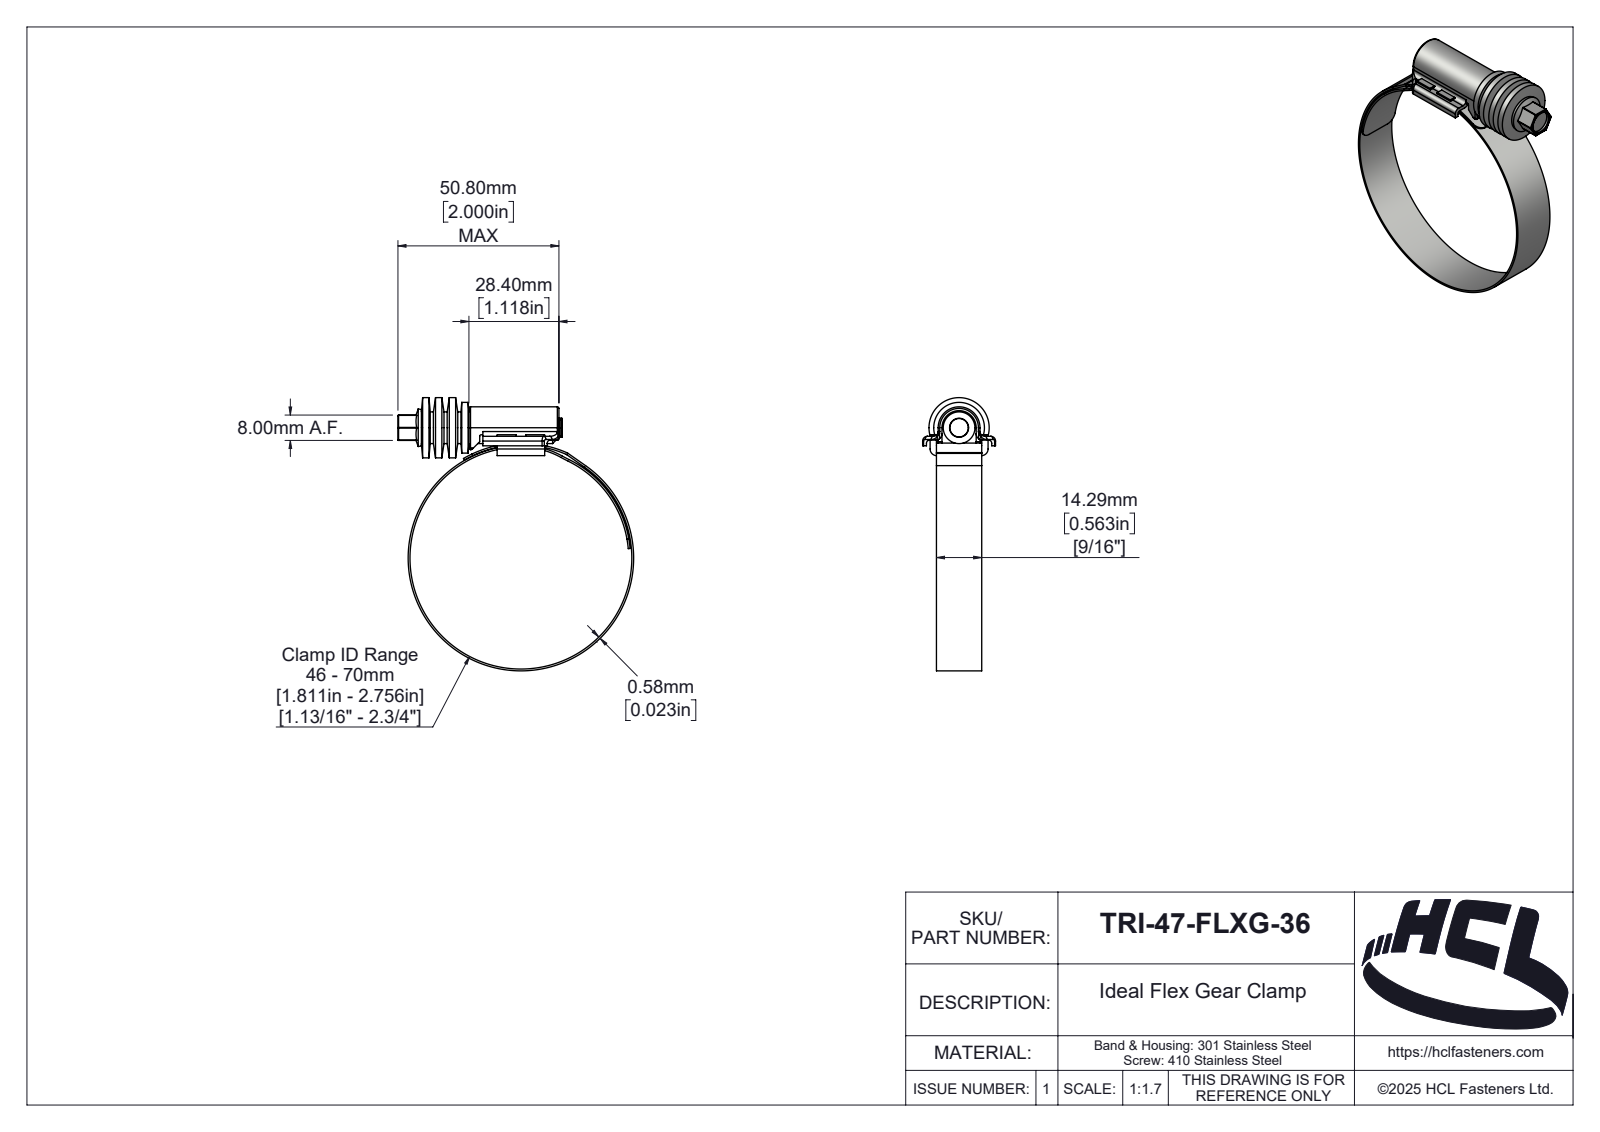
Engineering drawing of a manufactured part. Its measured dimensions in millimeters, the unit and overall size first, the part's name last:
Units: millimetres
Overall size (bounding box): 86.18 × 74.38 × 23
Round holes (diameter × count): ⌀7 ×1, ⌀70 ×1
Round bosses / shafts (diameter × count): ⌀71.16 ×1, ⌀19 ×1, ⌀16 ×1, ⌀10 ×1, ⌀6 ×1, ⌀5 ×1
Partial cylindrical surfaces — rounded edges, fillets, slot ends (radius × count): R0.2 ×12, R0.5 ×9, R1 ×8, R1.5 ×4, R3 ×4, R2 ×3, R0.1 ×2, R2.1 ×2
Main face-to-face distances: 2, 14.28, 1.2, 4.9, 1.74, 12.54, 16.29, 6.1, 0.58, 0.54
Volume: 9 999 mm³ · Surface area: 15 135 mm²
Bodies: 4 solids, 323 faces (88 planar, 139 cylindrical, 96 other)
Part name (STEP PRODUCT): TRI-47-FLXG-36
STEP written by: SolidWorks 2025 (AUTOMOTIVE_DESIGN)
